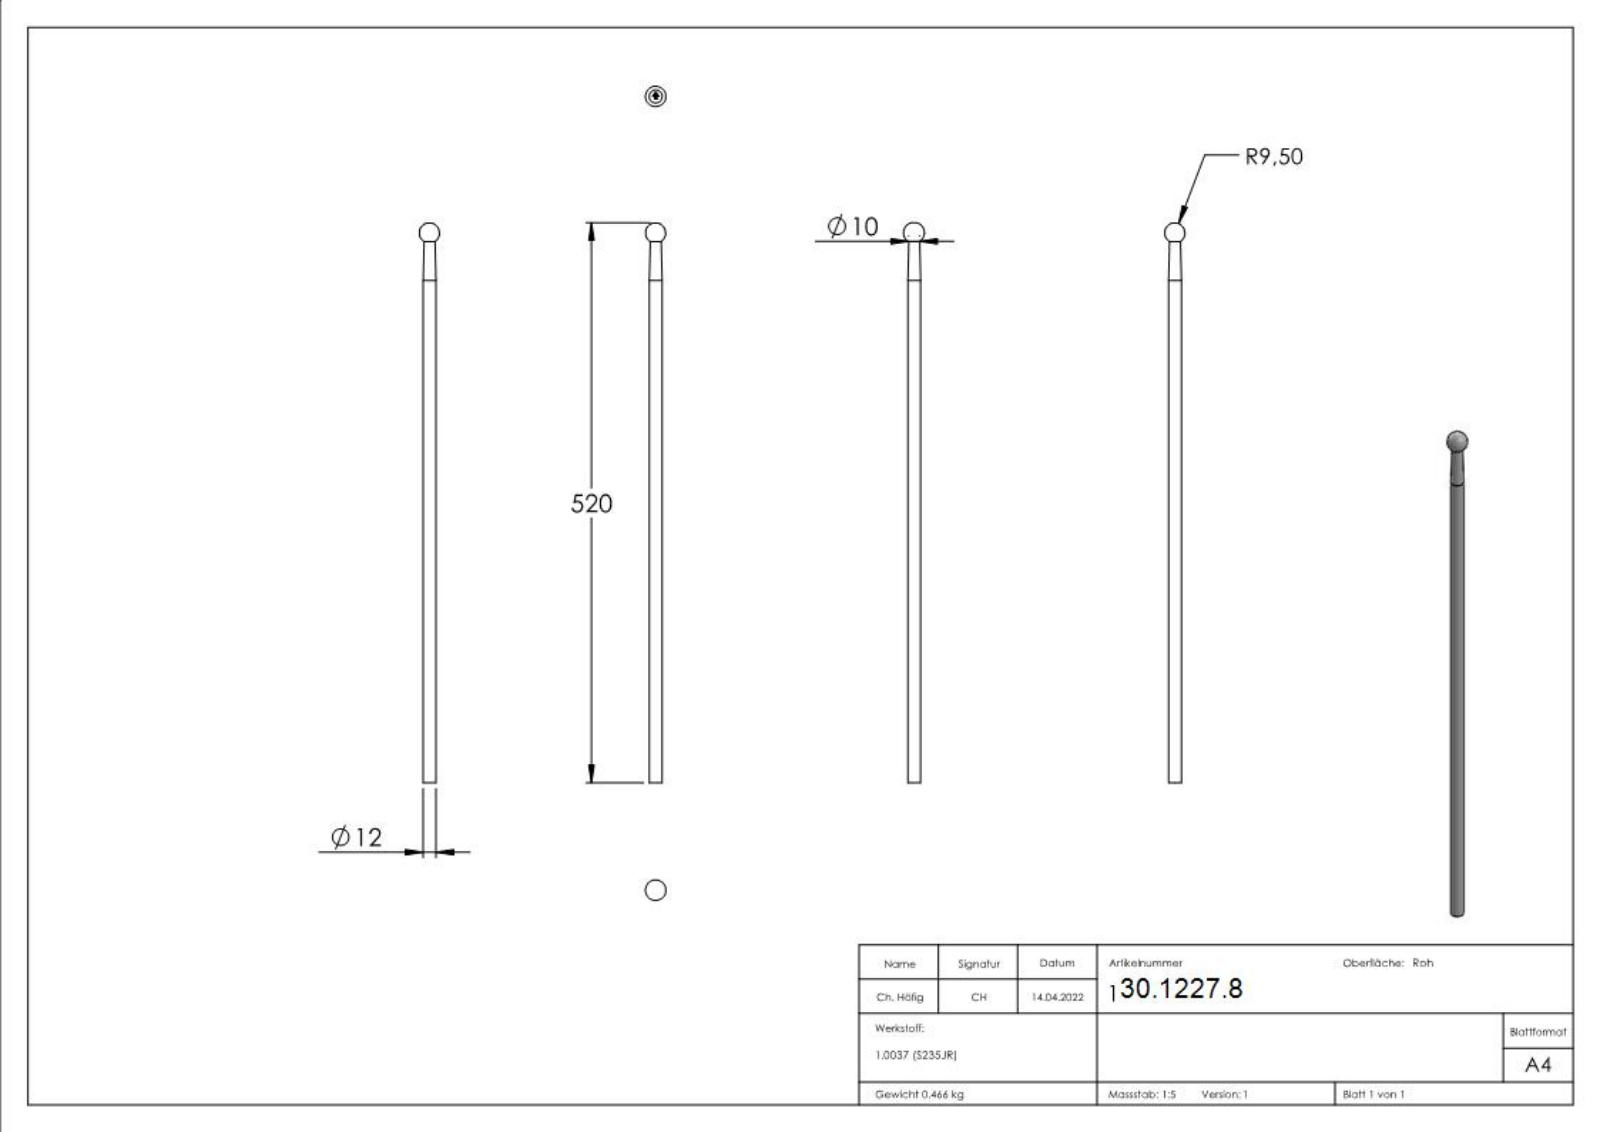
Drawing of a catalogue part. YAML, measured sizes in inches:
part_name: "1820"
step_written_by: "SolidWorks 2018 (CONFIG_CONTROL_DESIGN)"
units: inches
bodies: {solids: 1, faces: 211, planar: 108, cylindrical: 1, other: 102}
overall_size: [20.472, 0.748, 0.748]
volume: 3.644
surface_area: 31
round_bosses_or_shafts:
  - {diameter: 0.472, count: 1}
face_to_face_distances: [0.069, 0.091, 0.077, 0.019, 0.019, 0.064, 0.016, 0.07, 0.048, 0.033]
